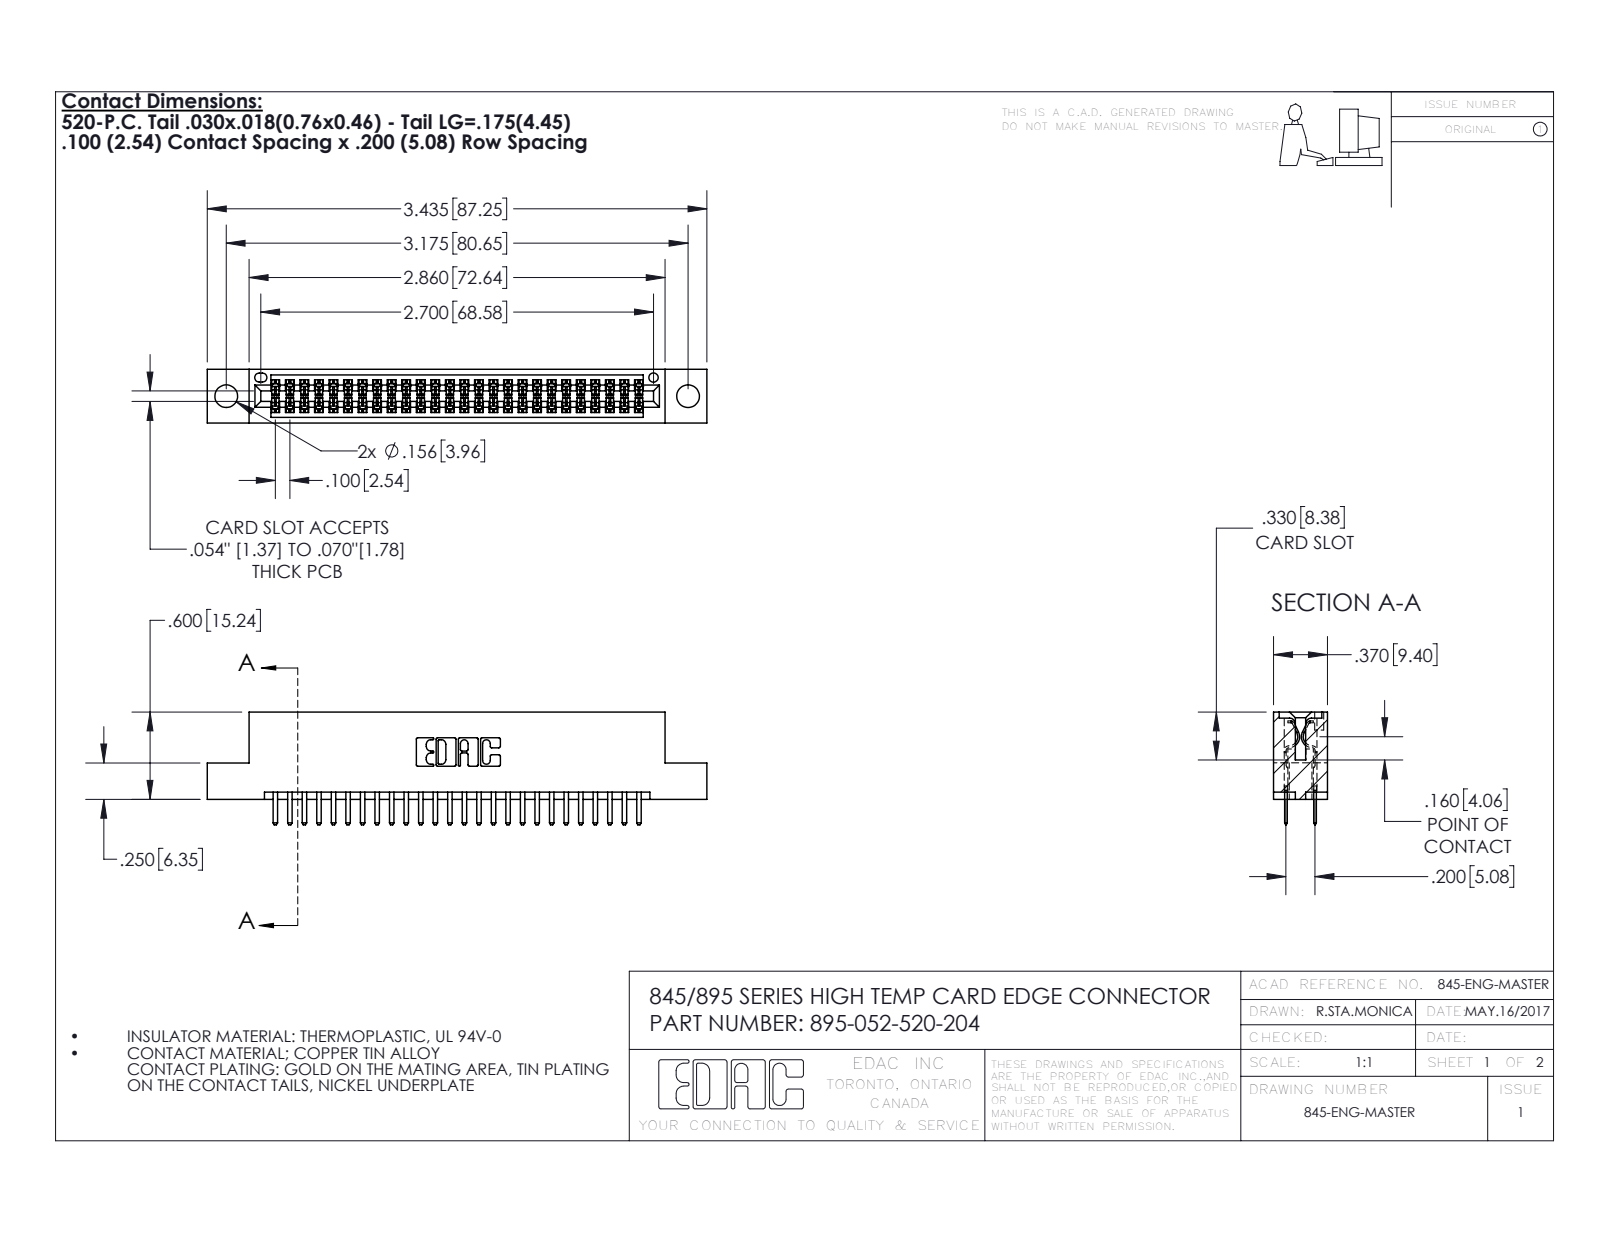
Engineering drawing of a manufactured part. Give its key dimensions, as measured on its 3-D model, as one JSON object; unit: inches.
{"part_name": "395-052-520-204; 345-292-001_345-293-120; 345 Part_Flush Mounting Lugs - 0.156 Dia-TH", "step_written_by": "SolidWorks 2016 (CONFIG_CONTROL_DESIGN)", "units": "inches", "bodies": {"solids": 53, "faces": 2934, "planar": 1900, "cylindrical": 1034, "other": 0}, "overall_size": [3.435, 0.775, 0.37], "volume_in3": 0.501, "surface_area_in2": 17.98, "round_holes": [[0.156, 2], [0.064, 1]], "partial_cylinders_radius": [[0.006, 78], [0.01, 56], [0.01, 22], [0.007, 6], [0.031, 6], [0.026, 3], [0.014, 2], [0.019, 2]], "face_to_face_distances": [0.298, 0.072, 0.2, 0.37, 0.098, 0.272, 0.025, 0.225, 0.022, 0.072], "hole_center_spacings": [0.27, 2.94, 3.175]}
